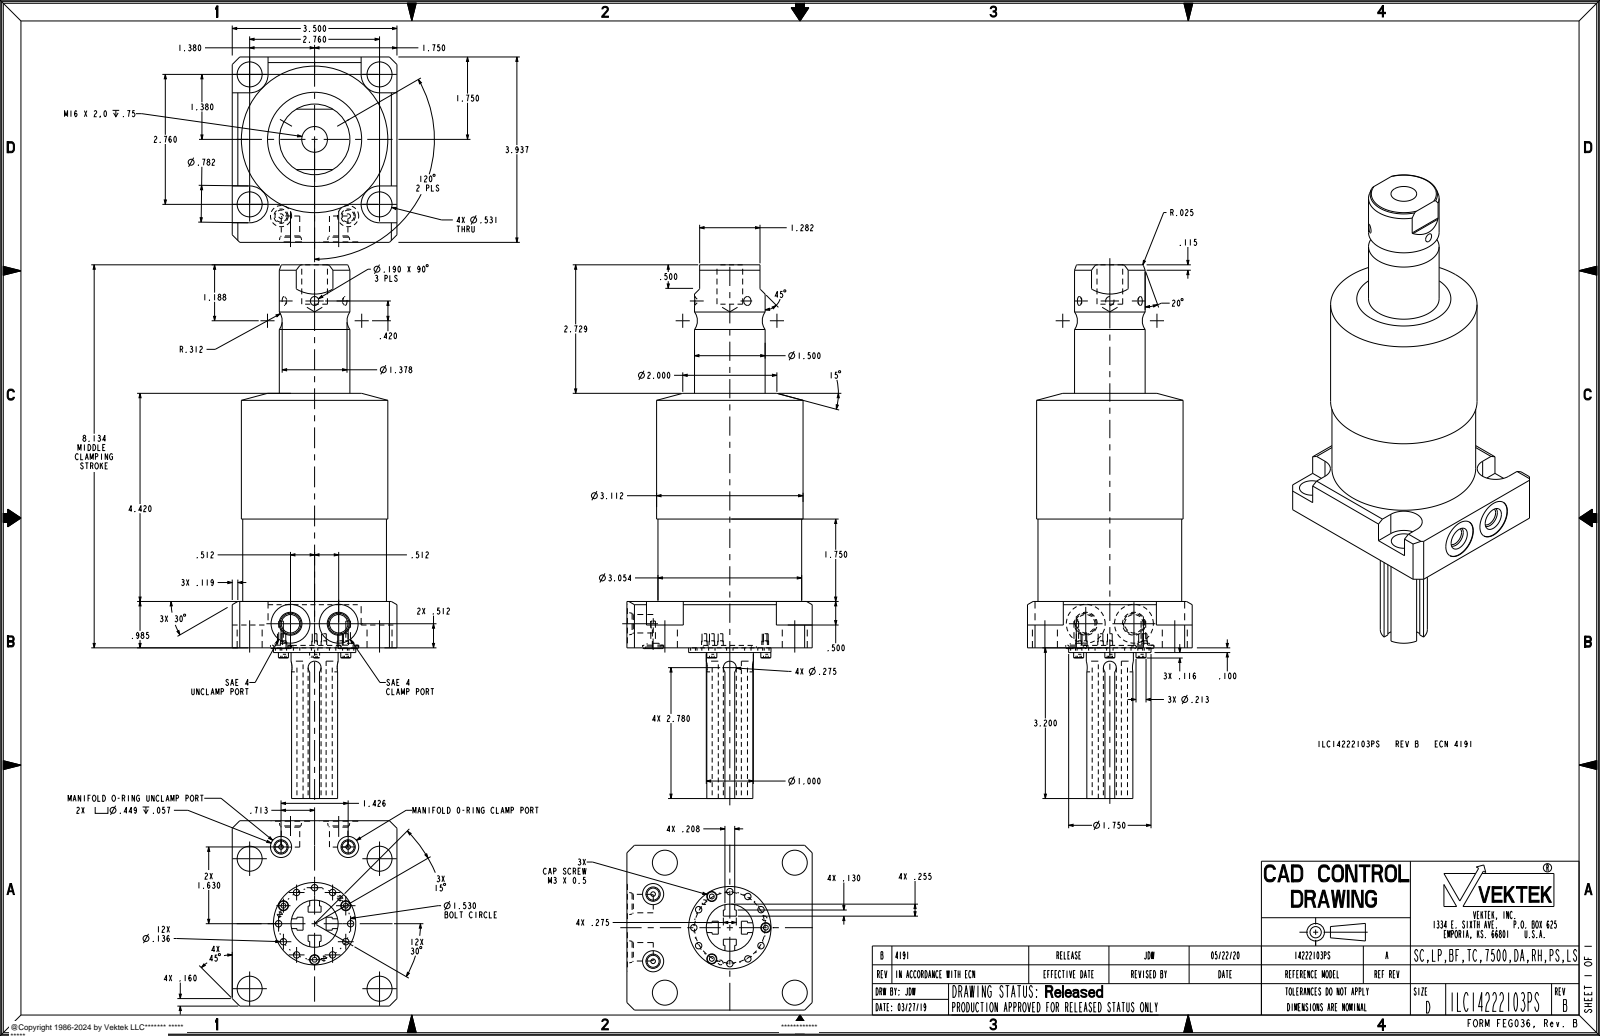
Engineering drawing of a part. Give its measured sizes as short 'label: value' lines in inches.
name: ILC14222103PS
written by: PRO/ENGINEER BY PARAMETRIC TECHNOLOGY CORPORATION, 2013320 (AUTOMOTIVE_DESIGN)
unit: in
bodies: 1 solid, 280 faces (130 planar, 112 cylindrical, 38 other)
size: 11.334 × 3.937 × 3.5
volume: 51 in³; area: 122.8 in²
holes: 12× ⌀0.136, 6× ⌀0.1, 4× ⌀0.531, 2× ⌀0.098, 2× ⌀0.256, 2× ⌀0.392, 2× ⌀0.449, 2× ⌀0.825, 1× ⌀0.546, 1× ⌀1.13
bosses: 6× ⌀0.118, 3× ⌀0.213, 1× ⌀3.112, 1× ⌀3.054, 1× ⌀1.75, 1× ⌀1.5, 1× ⌀1, 1× ⌀0.917
rounds: 4× R0.391, 2× R0.03, 2× R0.138
face distances: 0.985, 0.107, 0.382, 3.5, 0.141, 0.349, 0.033, 0.241, 1.995, 1.505
hole spacings: 0.765, 1.325, 0.396, 0.765, 1.082, 1.228, 1.478, 1.511
